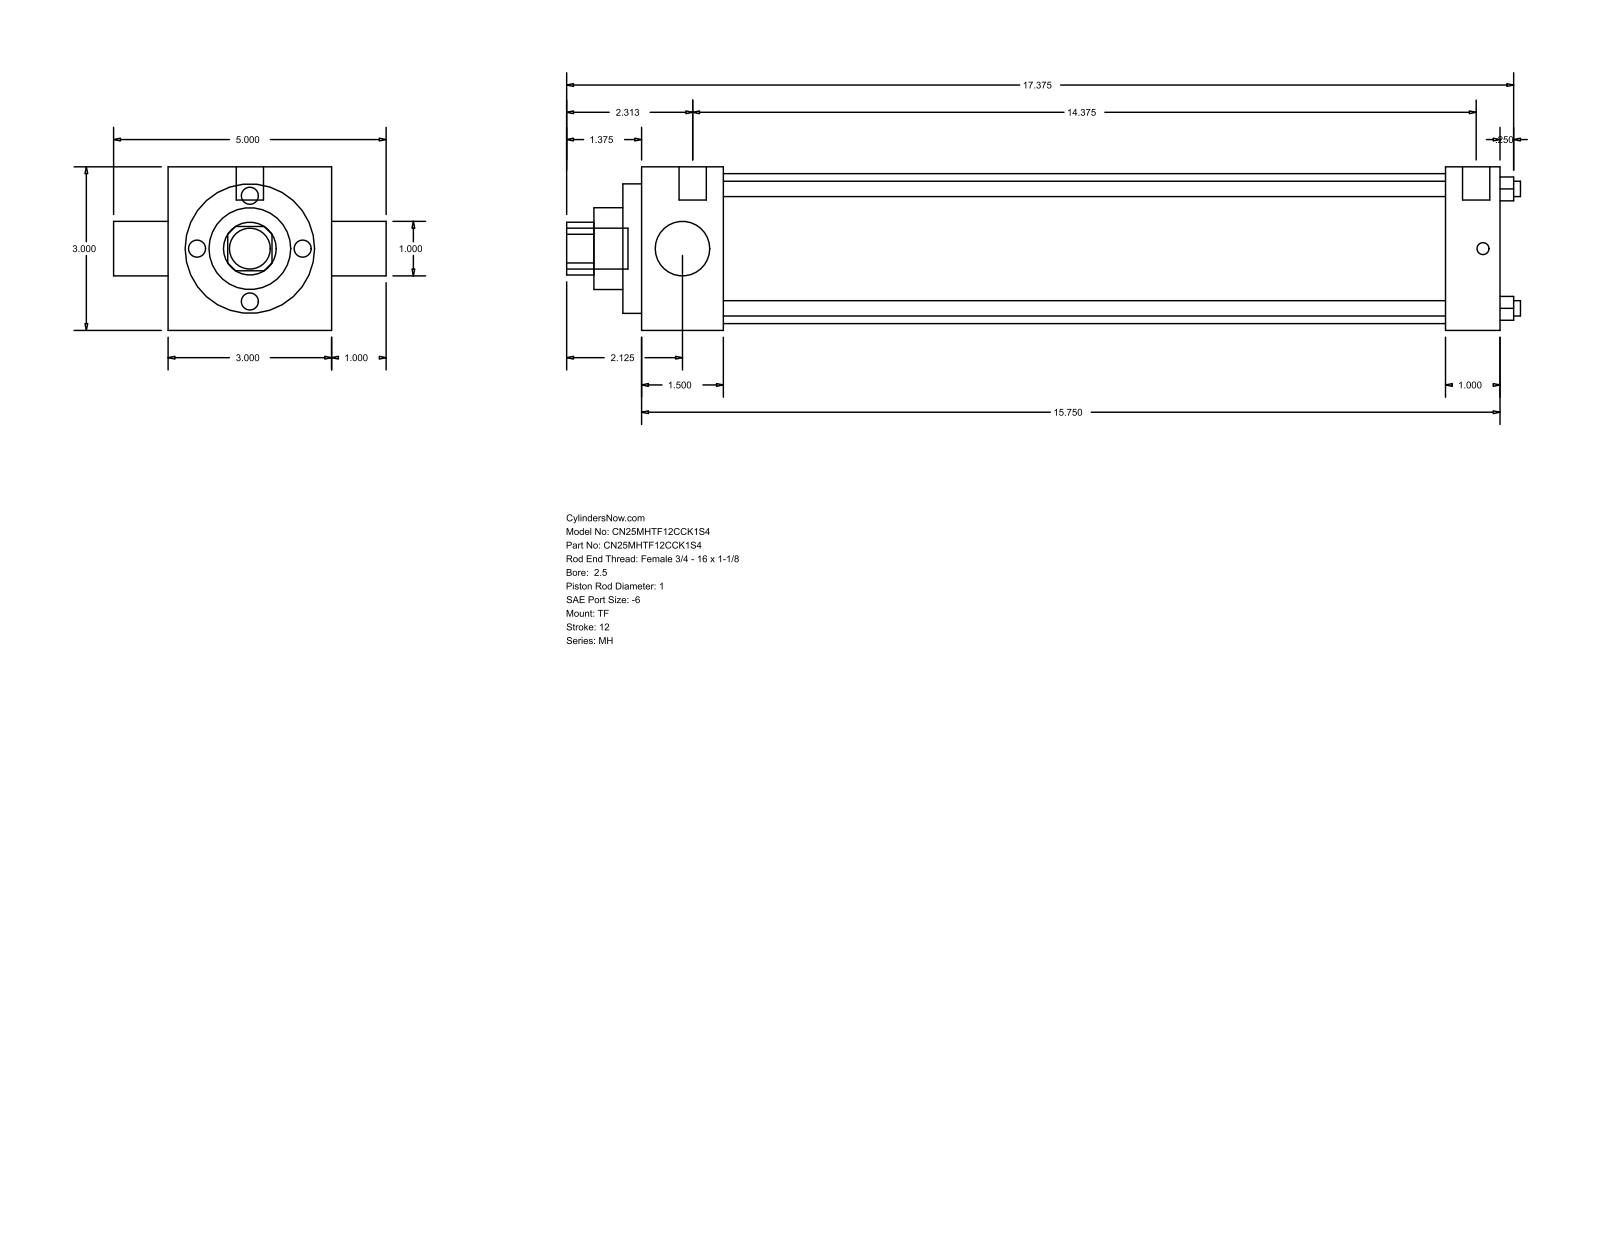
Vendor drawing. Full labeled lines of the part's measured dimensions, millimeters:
Part name (STEP PRODUCT): MH_TF__0250_1
STEP written by: GSSL Pune (CONFIG_CONTROL_DESIGN)
Units: millimetres
Bodies: 0 solids, 86 faces (61 planar, 25 cylindrical, 0 other)
Overall size (bounding box): 444.5 × 127 × 76.2
Round holes (diameter × count): ⌀7.14 ×4, ⌀25.4 ×2, ⌀38.1 ×1, ⌀60.33 ×1, ⌀69.85 ×1
Round bosses / shafts (diameter × count): ⌀5.56 ×3, ⌀12.7 ×2, ⌀19.05 ×1
Partial cylindrical surfaces — rounded edges, fillets, slot ends (radius × count): R12.29 ×1
Main face-to-face distances: 76.2, 400.06, 38.11, 361.95, 374.65, 336.54, 25.41, 8.73, 46.84, 383.38
Hole centre spacings: 39.33, 55.62, 78.66
